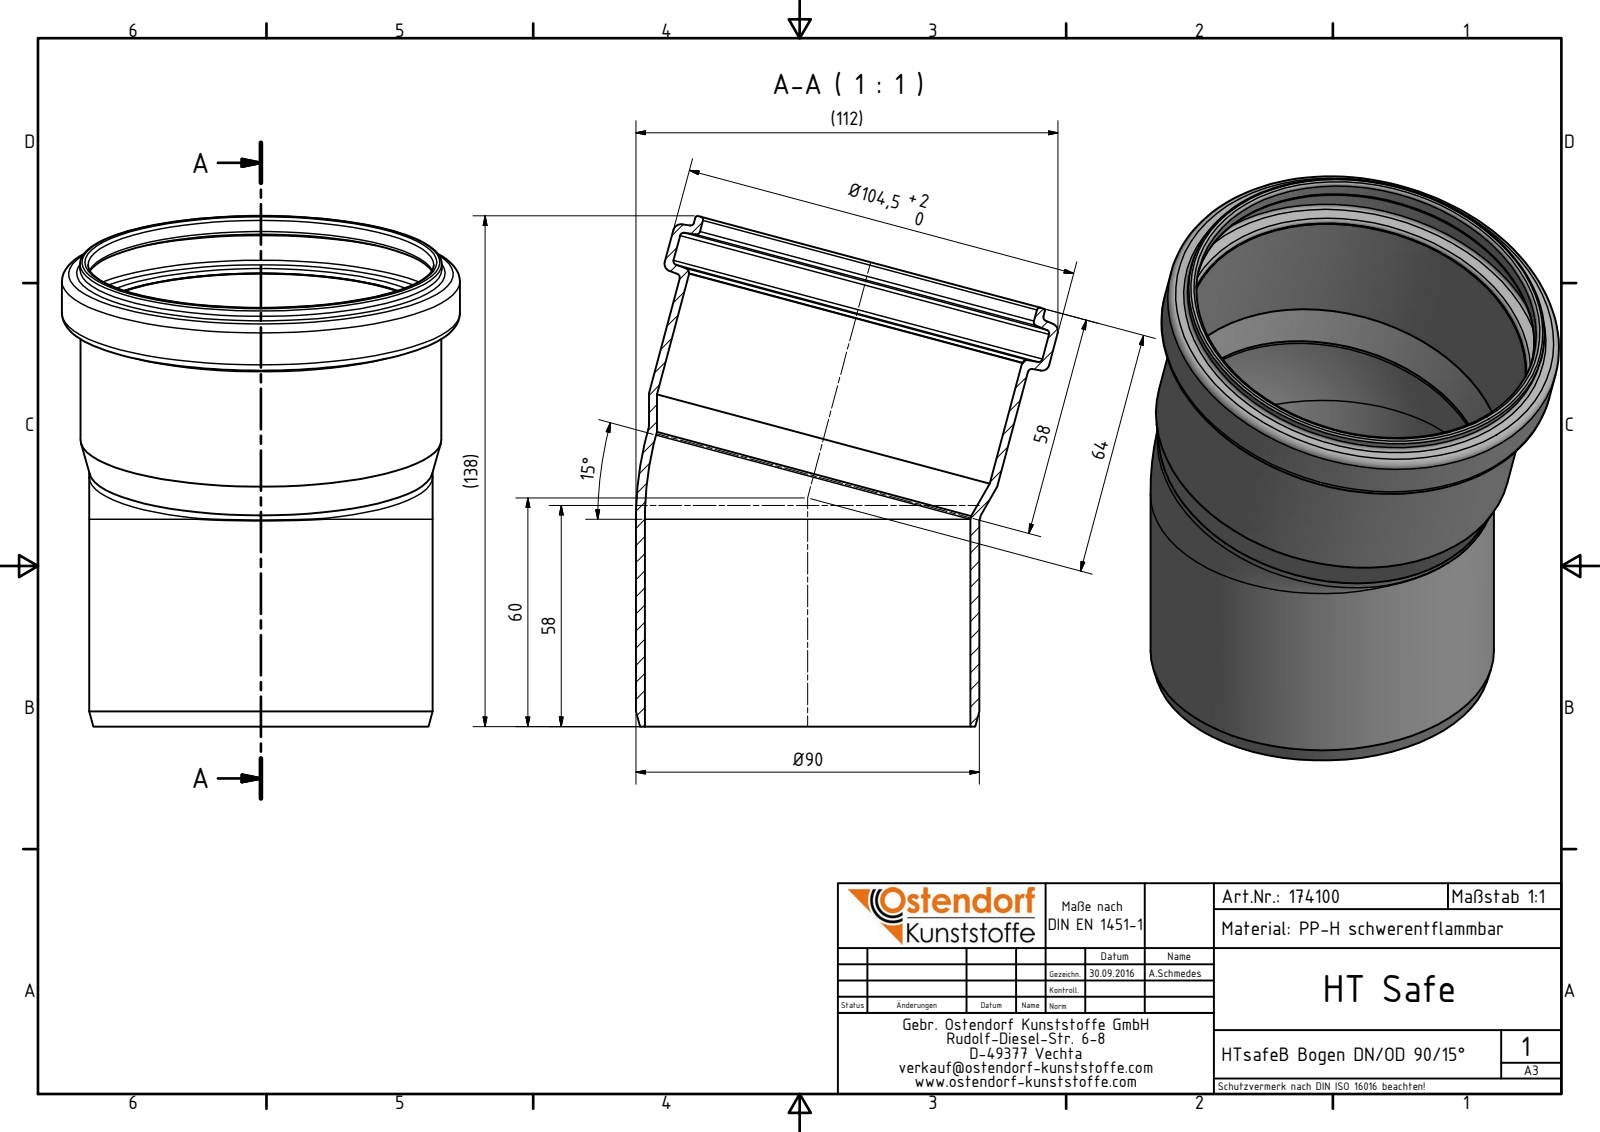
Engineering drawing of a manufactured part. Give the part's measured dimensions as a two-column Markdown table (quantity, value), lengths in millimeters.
| quantity | value |
| --- | --- |
| part name | 174100 HTsafeB DN_OD 90_15° |
| STEP written by | Autodesk Inventor 2016 (AUTOMOTIVE_DESIGN) |
| units | millimeters |
| bodies | 1 solid, 35 faces (4 planar, 11 cylindrical, 20 other) |
| overall size | 134 × 110.86 × 104.5 |
| volume | 83 414 mm³ |
| surface area | 75 966 mm² |
| round holes (diameter × count) | 85.44 × 2, 90.5 × 1, 90.8 × 1, 100.3 × 1 |
| round bosses / shafts (diameter × count) | 90.2 × 2, 104.5 × 1, 95 × 1, 94.7 × 1 |
| main face-to-face distances | 15.2, 42.32, 57.52 |
